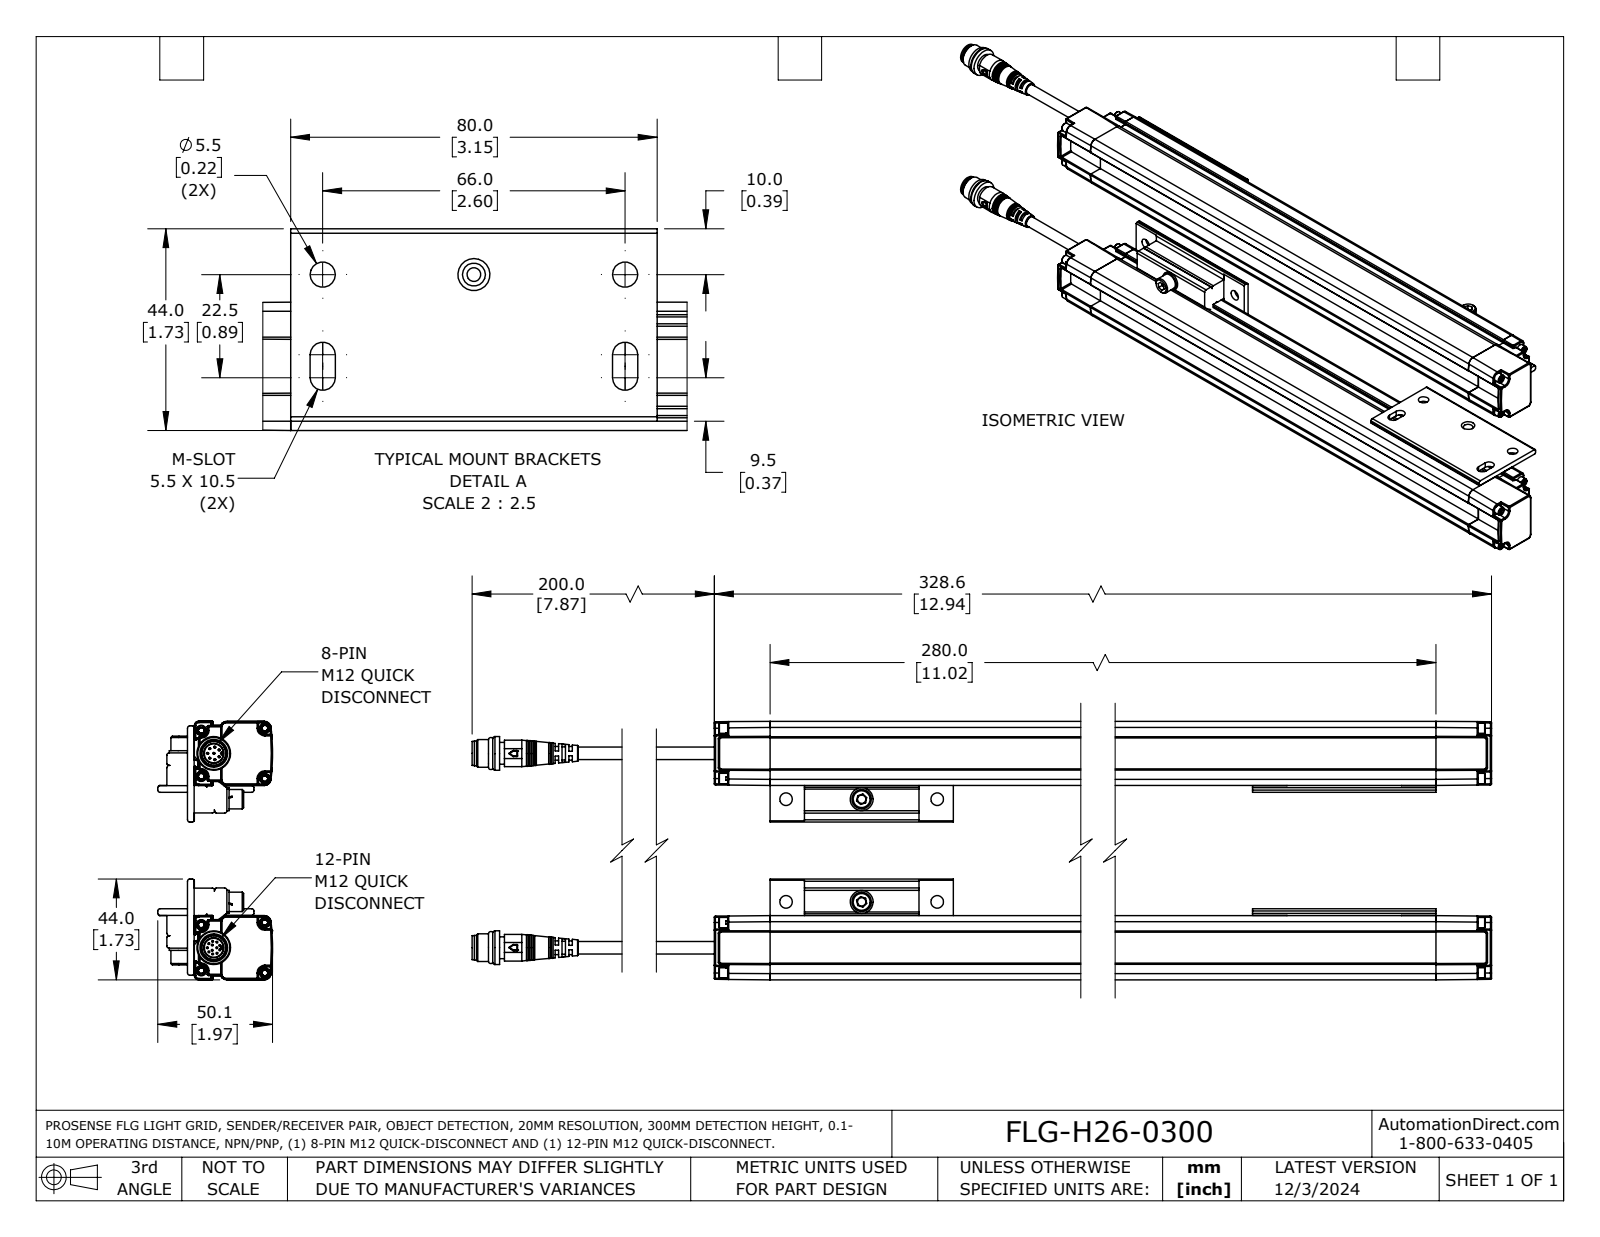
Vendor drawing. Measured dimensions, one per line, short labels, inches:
name: FLG-H26-0300
written by: SolidWorks 2023 (AUTOMOTIVE_DESIGN)
unit: in
bodies: 11 solids, 1671 faces (818 planar, 456 cylindrical, 397 other)
size: 16.557 × 4.441 × 1.972
volume: 35.54 in³; area: 269.3 in²
holes: 16× ⌀0.016, 6× ⌀0.217, 4× ⌀0.098, 3× ⌀0.197, 2× ⌀0.327
bosses: 20× ⌀0.031, 8× ⌀0.177, 8× ⌀0.118, 4× ⌀0.217, 4× ⌀0.059, 3× ⌀0.394, 3× ⌀0.335, 3× ⌀0.146
rounds: 142× R0.02, 40× R0.039, 20× R0.01, 12× R0.008, 12× R0.012, 12× R0.108, 6× R0.1, 4× R0.049
face distances: 3.339, 1.102, 0.118, 0.071, 0.189, 0.285, 0.817, 1.041, 2.236, 0.97
hole spacings: 0.108, 1.299, 0.163, 0.979, 2.191, 0.215, 1.764, 2.598
